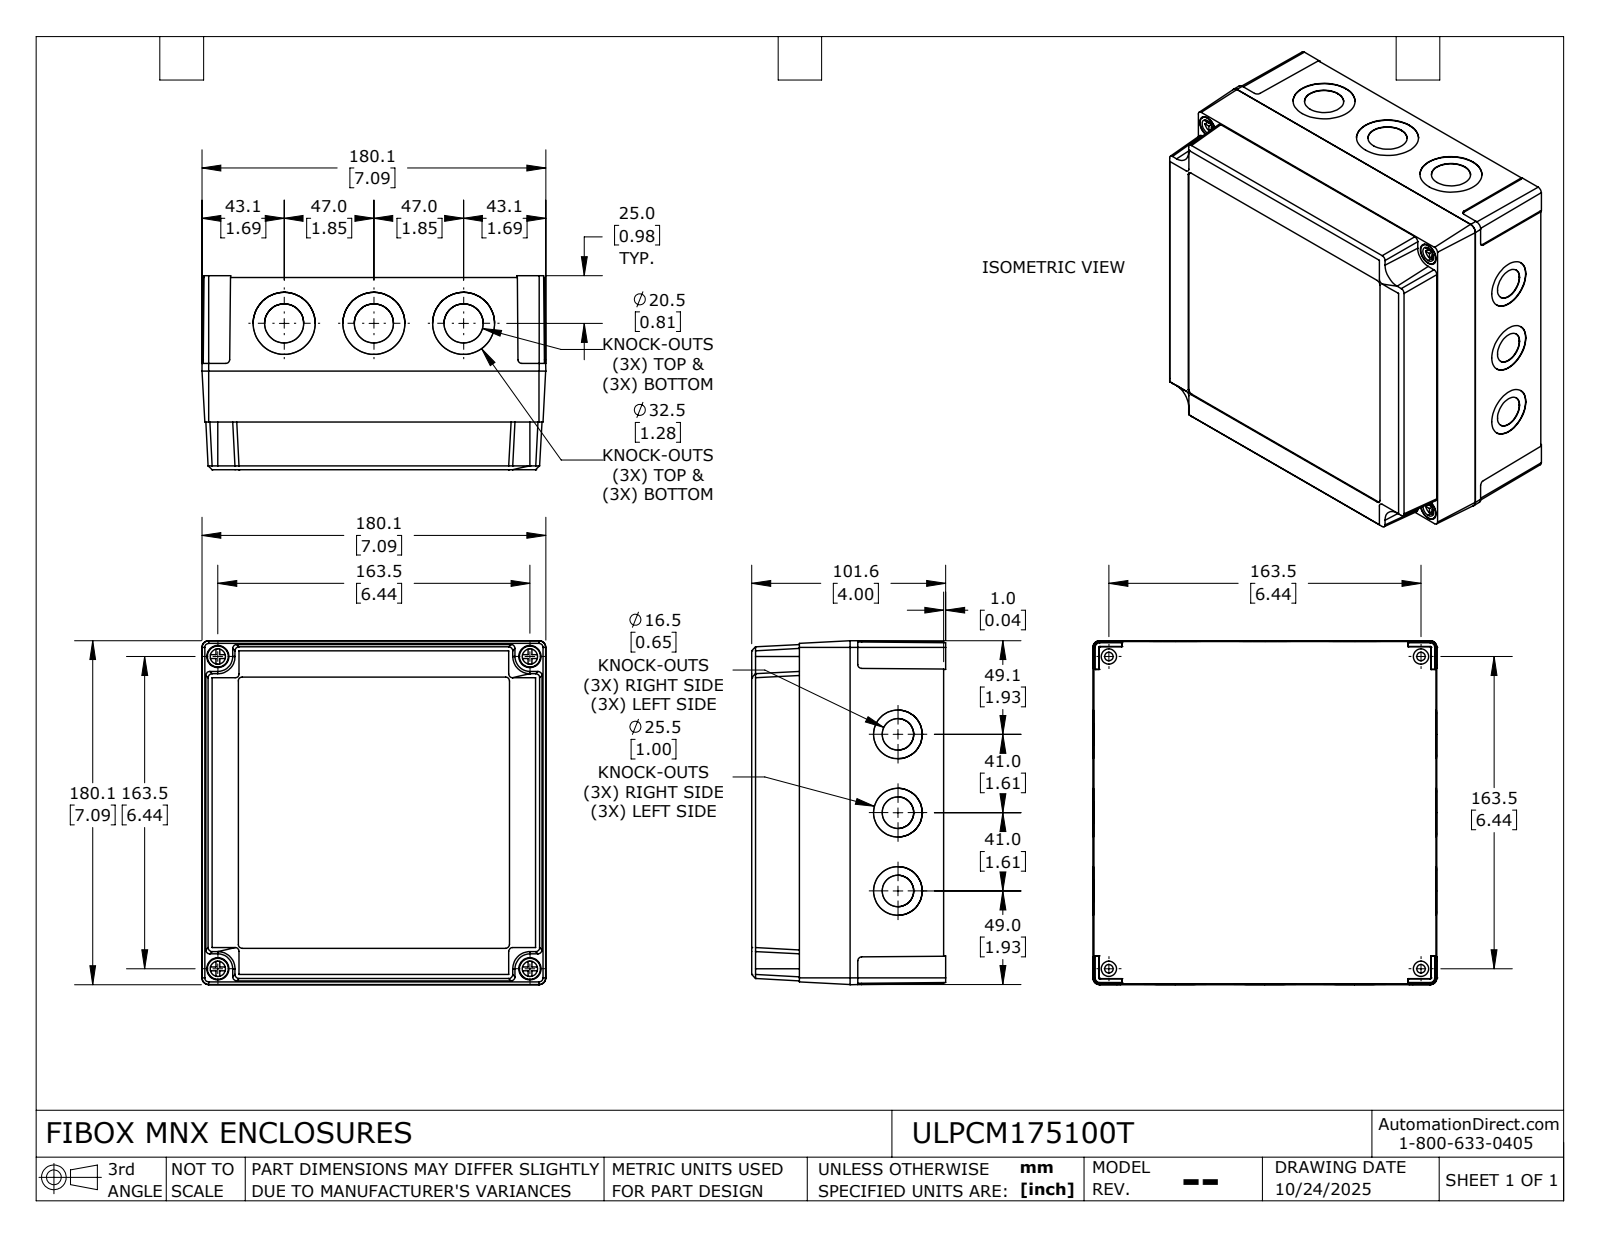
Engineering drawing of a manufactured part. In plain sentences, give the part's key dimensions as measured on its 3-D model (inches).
The part is named "ULPCM175100T_Default". Its 3-D file was written by "SolidWorks 2024 (CONFIG_CONTROL_DESIGN)". It is 6 solids with 629 faces: 351 planar, 232 cylindrical and 46 other. Overall it measures 7.091 by 7.091 by 4 inches. Its volume is 25.17 cubic inches and its surface area 430.7 square inches. Round holes: 12 of diameter 0.126, 12 of diameter 0.157, 6 of diameter 0.65, 6 of diameter 0.807, 6 of diameter 1.004, 6 of diameter 1.28, 4 of diameter 0.177, 4 of diameter 0.315, 4 of diameter 0.457. Round bosses or shafts: 12 of diameter 0.315, 8 of diameter 0.098, 4 of diameter 0.433, 4 of diameter 0.283. Partial cylindrical surfaces (rounded edges, fillets, slot ends): 8 of radius 0.079, 8 of radius 0.083, 6 of radius 0.112, 4 of radius 0.042, 4 of radius 0.197, 2 of radius 0.046. The main face-to-face distances are 3.85, 0.118, 3.732, 0.165, 0.091, 3.941, 3.823, 0.077, 0.055, 0.022. The hole center spacings are 1.333, 1.969, 2.866, 3.252, 4.79, 5.207, 5.469, 5.853.
